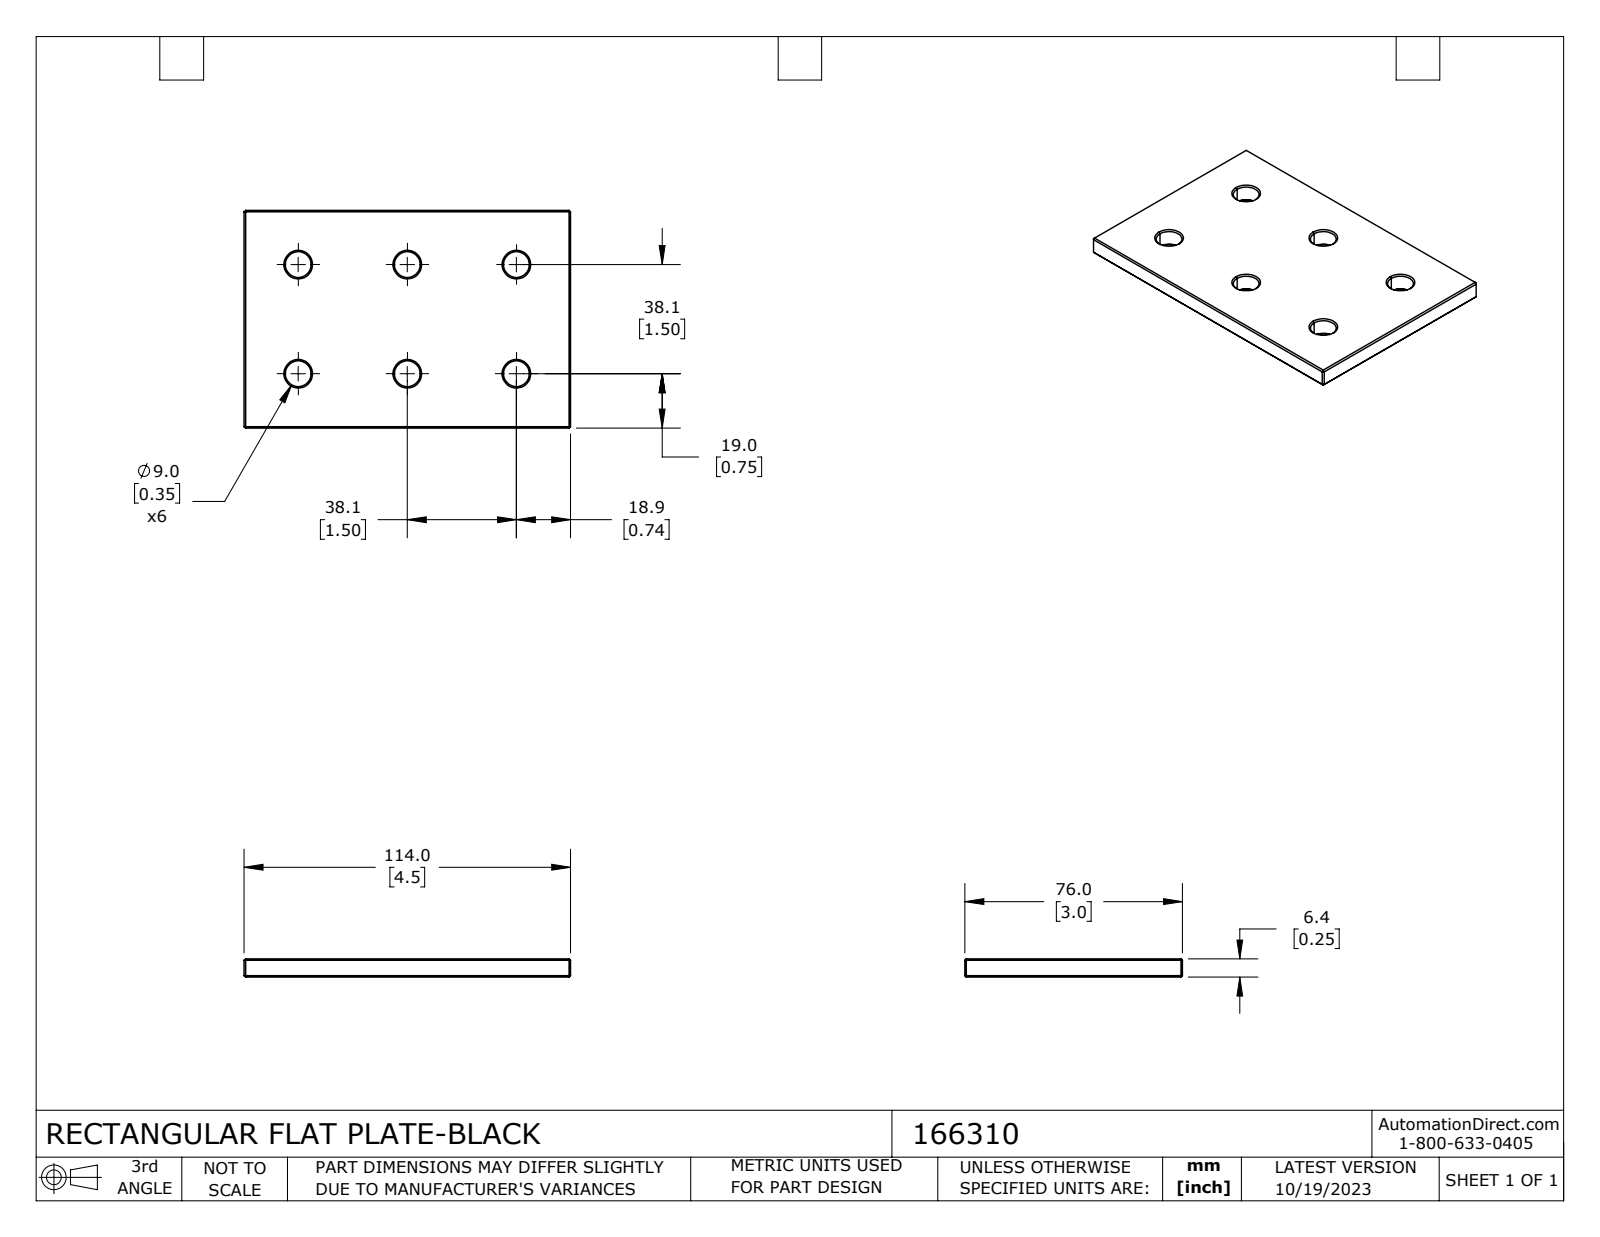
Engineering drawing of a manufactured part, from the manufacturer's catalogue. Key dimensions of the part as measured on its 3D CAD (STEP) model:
Part name (STEP PRODUCT): 166310
STEP written by: SolidWorks 2023 (CONFIG_CONTROL_DESIGN)
Units: millimetres
Bodies: 1 solid, 62 faces (26 planar, 12 cylindrical, 24 other)
Overall size (bounding box): 114 × 76 × 6.35
Volume: 52 451 mm³ · Surface area: 19 729 mm²
Round holes (diameter × count): ⌀9 ×6
Main face-to-face distances: 6.35, 76, 114, 57.51, 84.38, 133.62, 112.14
Hole centre spacings: 38.1, 53.88, 76.2, 85.19
